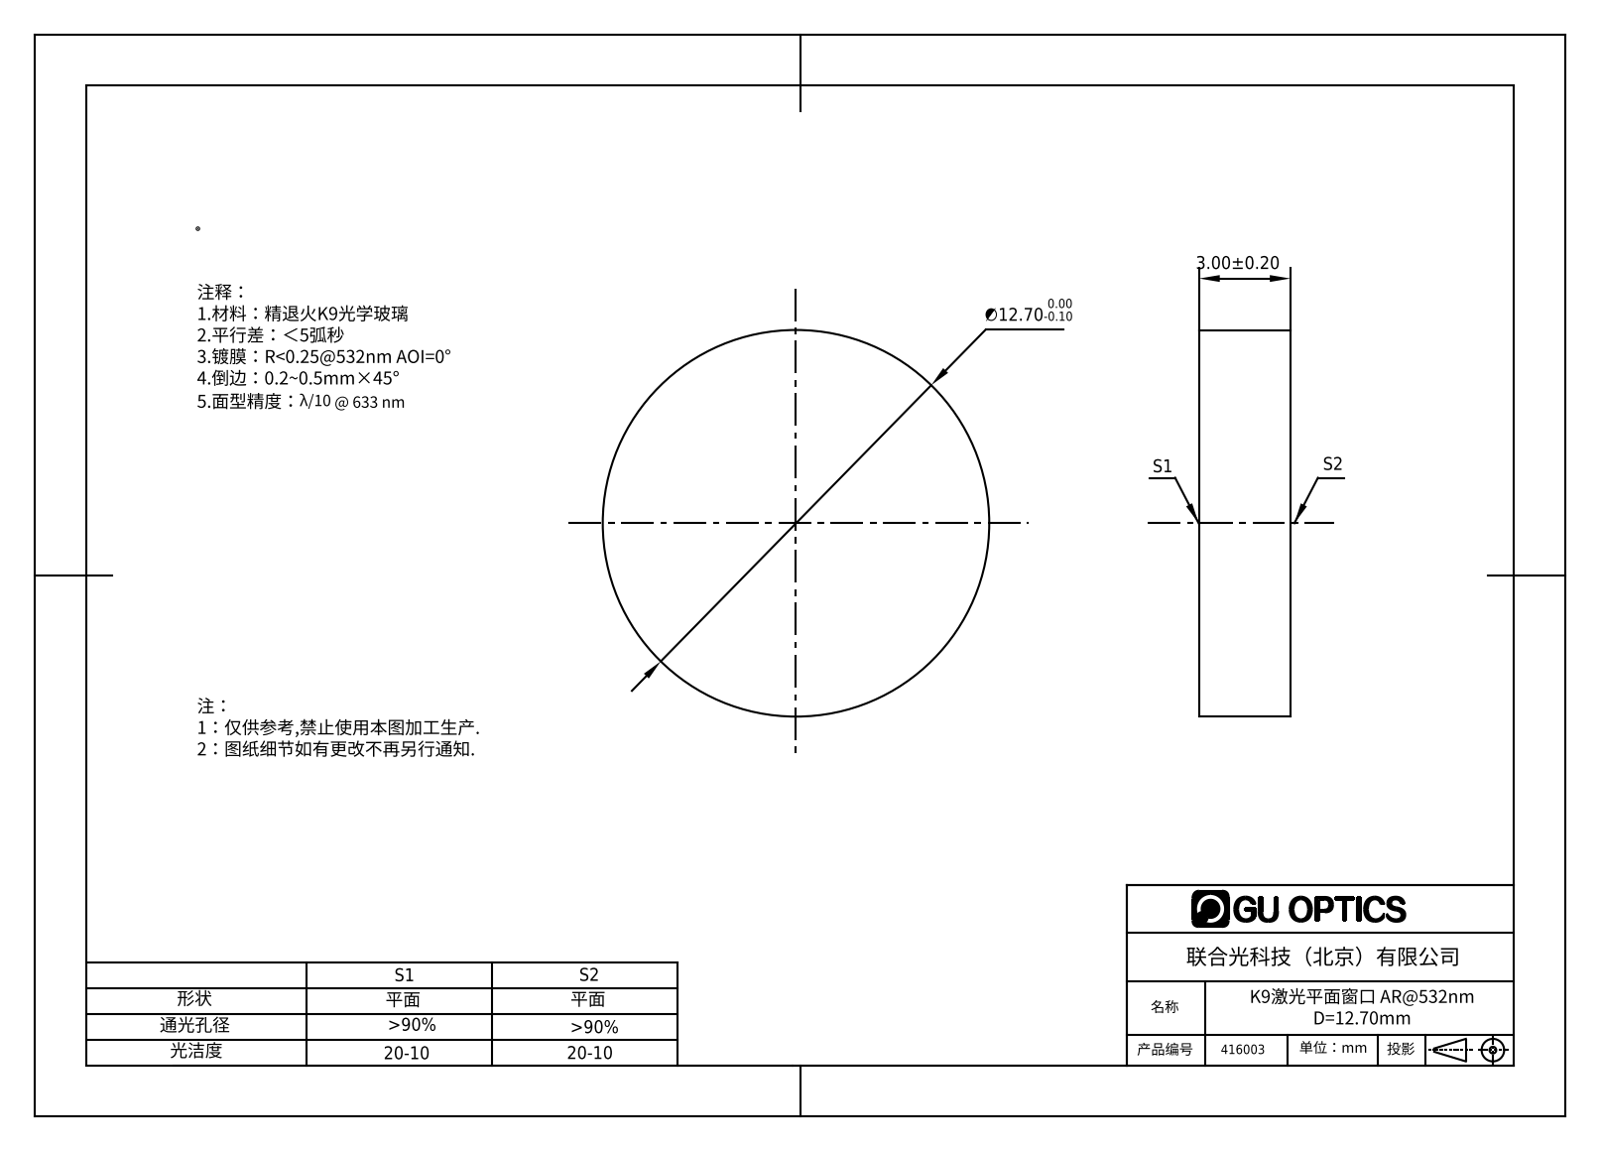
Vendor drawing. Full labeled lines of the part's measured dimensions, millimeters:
Part name (STEP PRODUCT): 416003
STEP written by: SolidWorks 2016 (CONFIG_CONTROL_DESIGN)
Units: millimetres
Bodies: 1 solid, 4 faces (2 planar, 2 cylindrical, 0 other)
Overall size (bounding box): 12.7 × 12.7 × 3
Volume: 380 mm³ · Surface area: 373 mm²
Round bosses / shafts (diameter × count): ⌀12.7 ×1
Main face-to-face distances: 3
